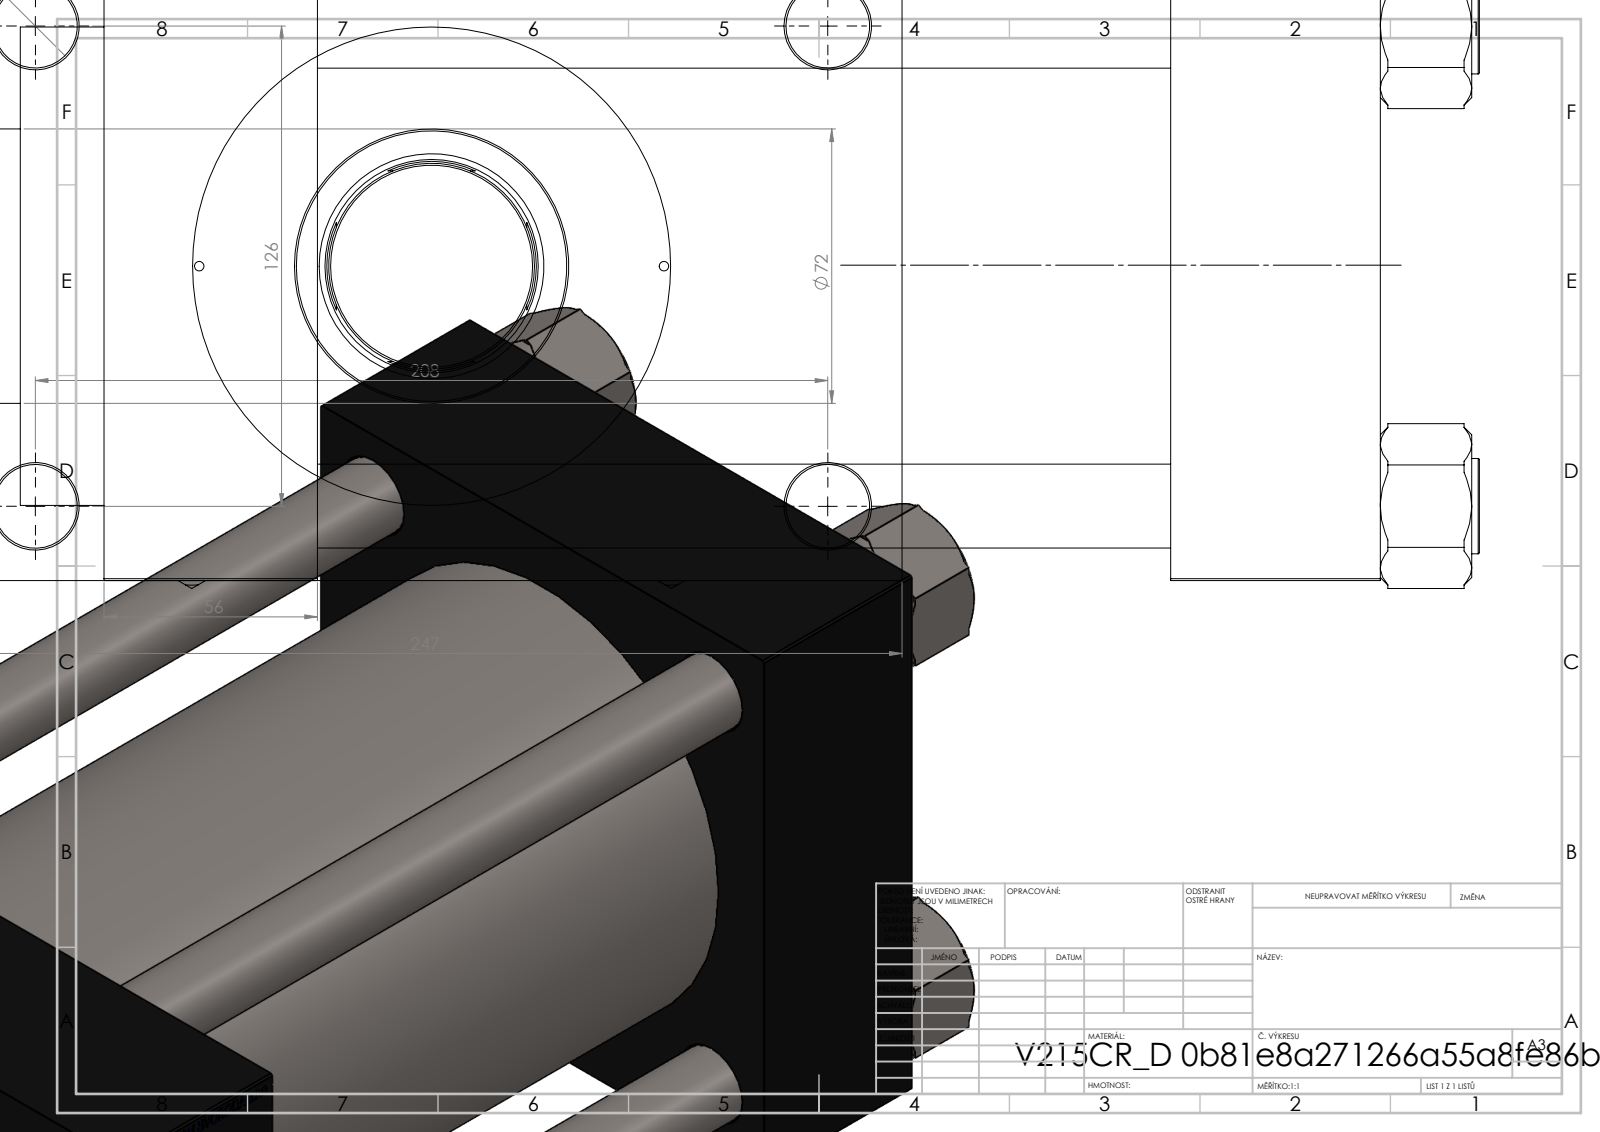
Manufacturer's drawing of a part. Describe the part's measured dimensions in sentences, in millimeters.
The part is named "V215CR_ROD_END_F; V215CR_VCP_D; V215CR_D_TYCINKA; V215_VC_A (+2 more)". Its 3-D file was written by "SolidWorks 2019 (CONFIG_CONTROL_DESIGN)". It is 12 solids with 1168 faces: 550 planar, 94 cylindrical and 524 other. Overall it measures 470 by 247 by 169.14 millimeters. Its volume is 5 743 000 cubic millimeters and its surface area 722 606 square millimeters. Round holes: 8 of diameter 22, 2 of diameter 2.5, 2 of diameter 7, 2 of diameter 32.24, 2 of diameter 45, 1 of diameter 40.5, 1 of diameter 56, 1 of diameter 59, 1 of diameter 96, 1 of diameter 125, 1 of diameter 125.5. Round bosses or shafts: 4 of diameter 25, 1 of diameter 131, 1 of diameter 72, 1 of diameter 54, 1 of diameter 40. The main face-to-face distances are 165, 224, 55, 279, 56, 335, 280, 41, 206, 313.74. The hole center spacings are 41.05, 62.98, 76.28, 89.02, 121.59, 125.9, 132.47, 139.02.
